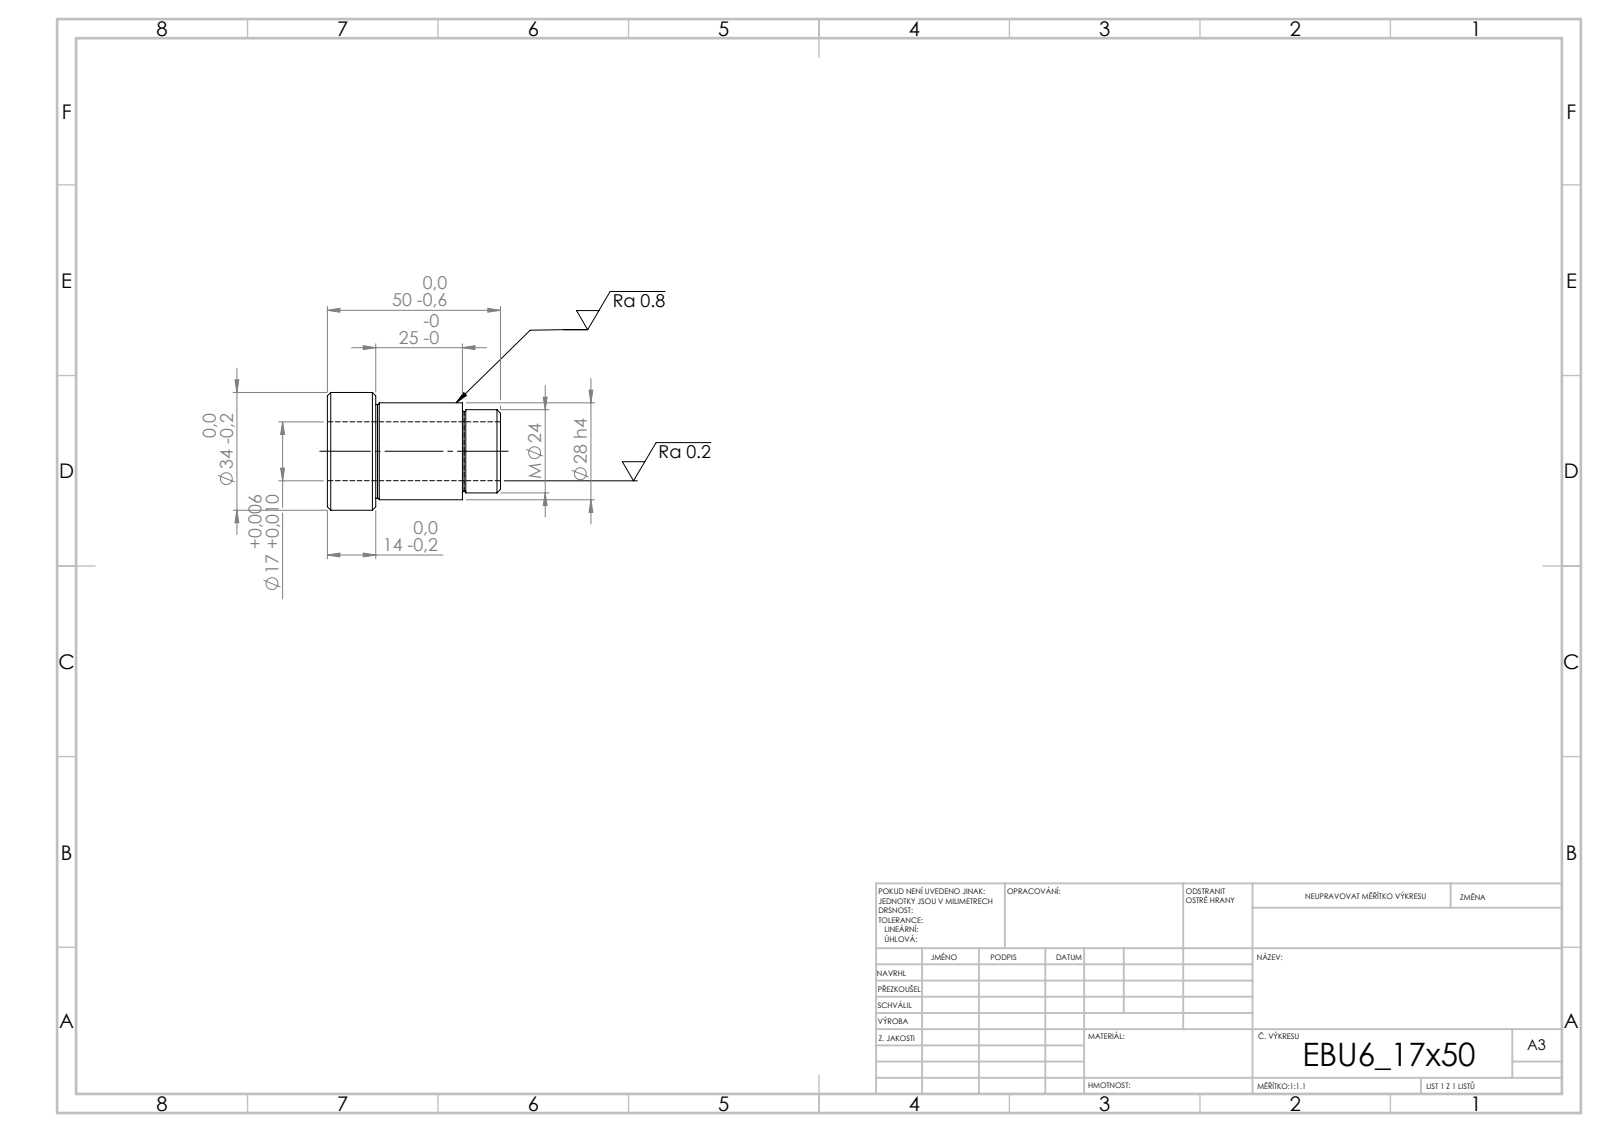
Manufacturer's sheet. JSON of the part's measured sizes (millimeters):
{"step_written_by": "SolidWorks 2019 (CONFIG_CONTROL_DESIGN)", "units": "millimeters", "bodies": {"solids": 1, "faces": 27, "planar": 5, "cylindrical": 12, "other": 10}, "overall_size": [50, 34, 34], "volume_mm3": 21519, "surface_area_mm2": 8503, "round_holes": [[17, 1]], "round_bosses_or_shafts": [[34, 1], [28, 1], [27, 1], [24, 1], [23, 1]], "face_to_face_distances": [14, 25, 39, 11, 36, 50, 10, 1, 26, 40]}
